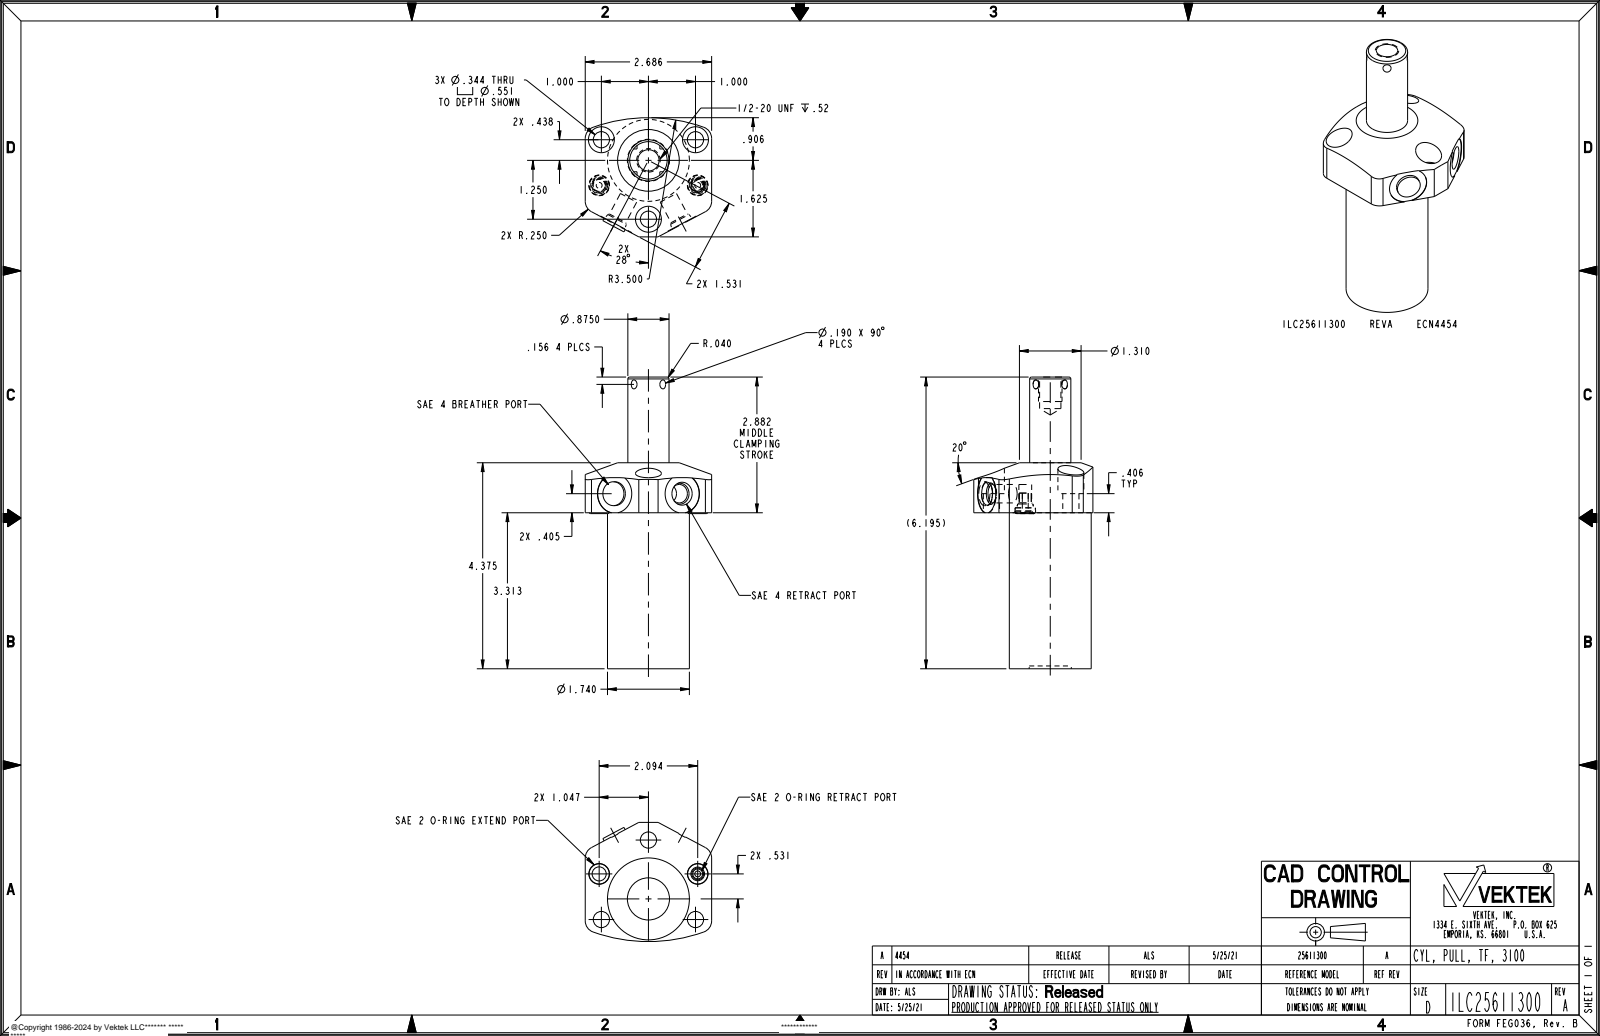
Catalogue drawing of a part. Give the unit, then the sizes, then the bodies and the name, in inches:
Units: inches
Overall size (bounding box): 6.195 × 2.686 × 2.531
Round holes (diameter × count): ⌀0.344 ×3, ⌀0.551 ×3, ⌀0.125 ×2, ⌀0.272 ×2, ⌀0.392 ×2, ⌀0.438 ×2, ⌀0.453 ×1, ⌀0.895 ×1
Round bosses / shafts (diameter × count): ⌀0.43 ×2, ⌀0.256 ×2, ⌀1.74 ×1, ⌀0.875 ×1, ⌀0.507 ×1, ⌀0.5 ×1, ⌀0.21 ×1
Partial cylindrical surfaces — rounded edges, fillets, slot ends (radius × count): R0.25 ×4, R0.412 ×2, R3.5 ×1
Main face-to-face distances: 3.313, 2.686, 4.375, 1.062, 0.06, 3.253, 4.315, 3.719, 3.659, 0.406
Hole centre spacings: 0.97, 1.092, 1.174, 1.27, 1.962, 2.265, 1.25, 2
Volume: 13.65 in³ · Surface area: 52.02 in²
Bodies: 1 solid, 131 faces (36 planar, 59 cylindrical, 36 other)
Part name (STEP PRODUCT): ILC25611300
STEP written by: PRO/ENGINEER BY PARAMETRIC TECHNOLOGY CORPORATION, 2013320 (CONFIG_CONTROL_DESIGN)
